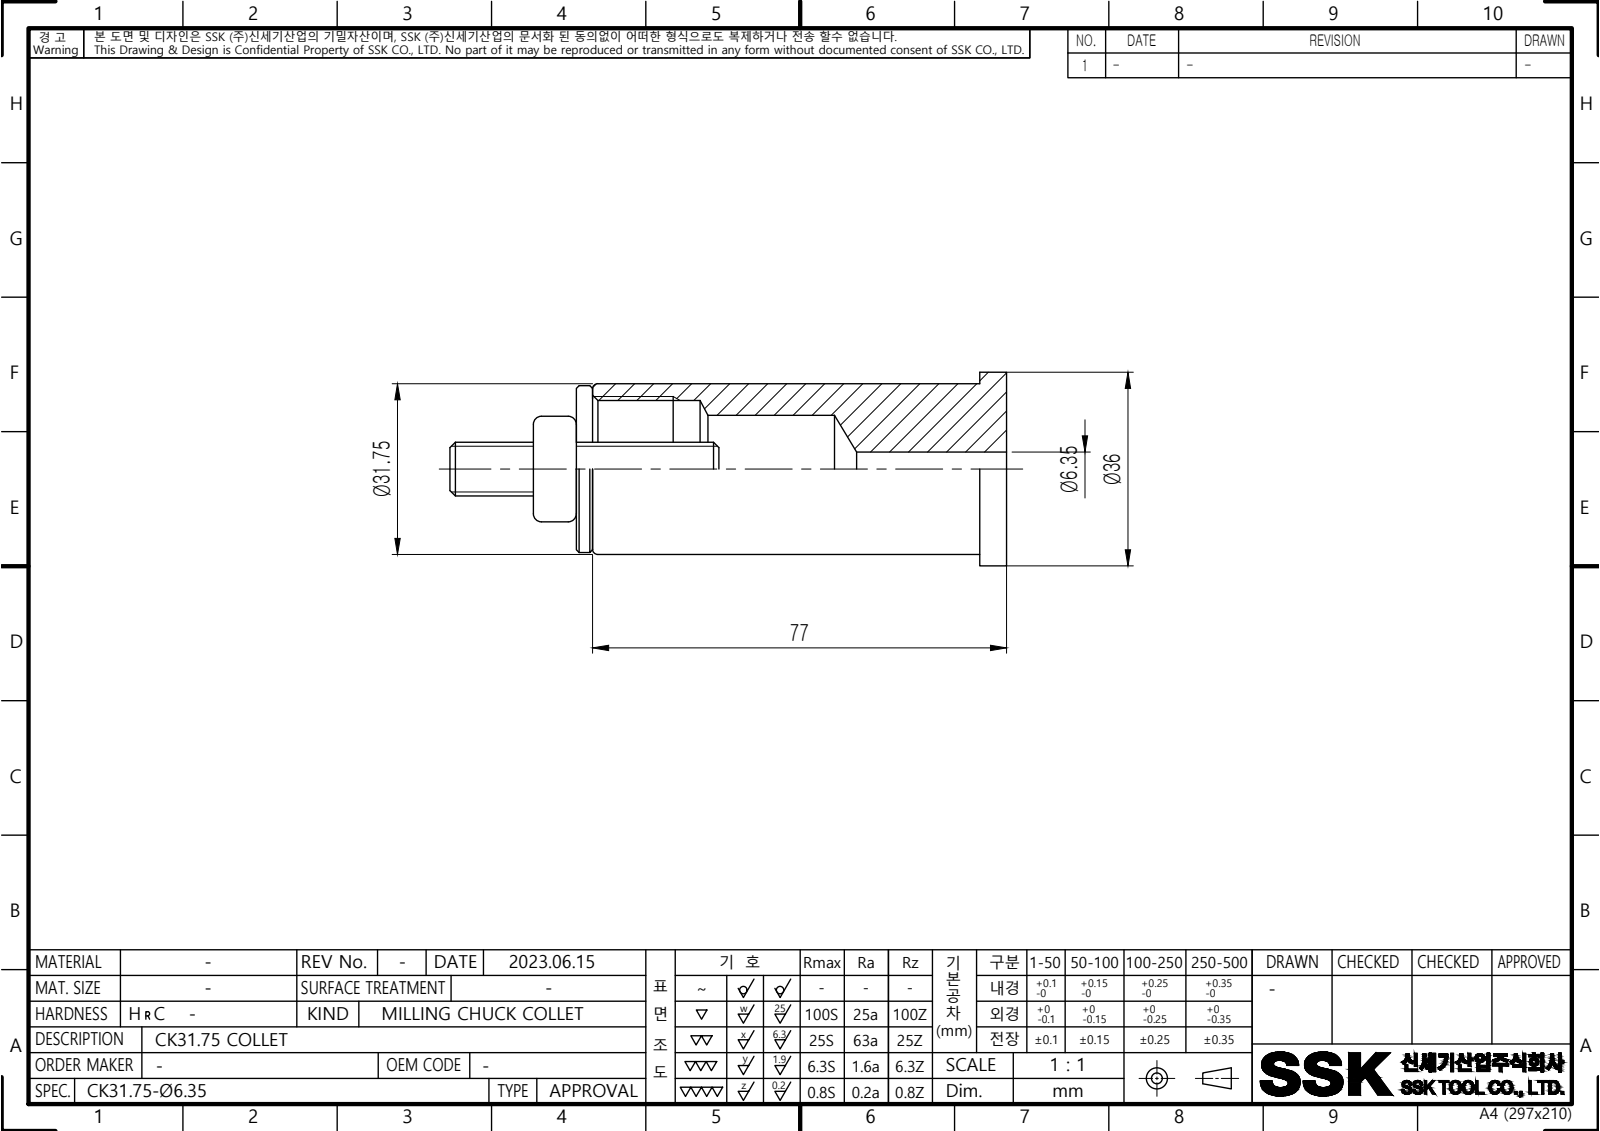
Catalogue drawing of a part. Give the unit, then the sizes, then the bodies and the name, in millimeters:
Units: millimetres
Overall size (bounding box): 77 × 36 × 36
Round holes (diameter × count): ⌀6.35 ×1, ⌀20 ×1, ⌀25.38 ×1
Round bosses / shafts (diameter × count): ⌀36 ×1, ⌀31.75 ×1
Main face-to-face distances: 77, 72, 5
Volume: 42 484 mm³ · Surface area: 13 419 mm²
Bodies: 1 solid, 10 faces (3 planar, 5 cylindrical, 2 other)
Part name (STEP PRODUCT): LO-CK31.75-6.35
STEP written by: Autodesk Inventor 2022 (AUTOMOTIVE_DESIGN)
